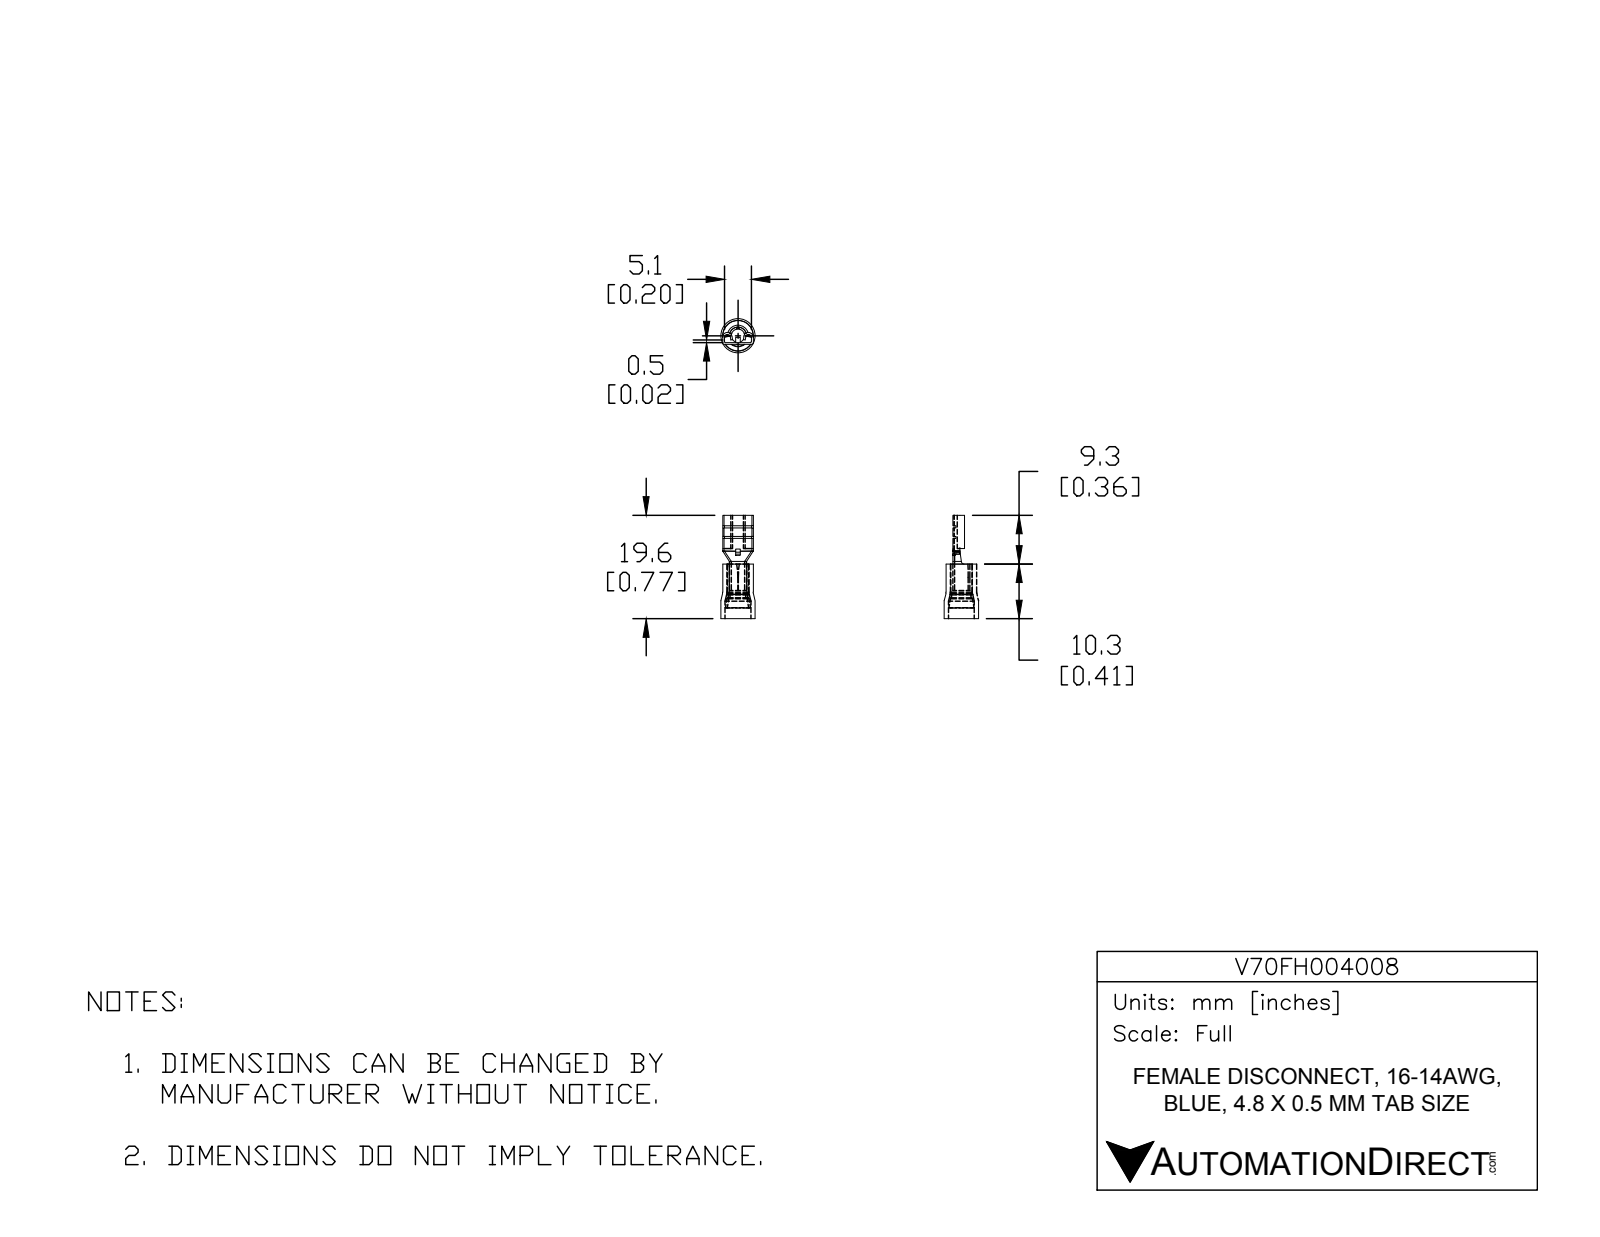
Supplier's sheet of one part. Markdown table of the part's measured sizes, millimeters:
| quantity | value |
| --- | --- |
| part name | V70FH004008 |
| STEP written by | SolidWorks 2017 (AUTOMOTIVE_DESIGN) |
| units | millimeters |
| bodies | 3 solids, 121 faces (49 planar, 38 cylindrical, 34 other) |
| overall size | 19.59 × 6.49 × 6.49 |
| volume | 220 mm³ |
| surface area | 890 mm² |
| round holes (diameter × count) | 2.55 × 1, 3.3 × 1, 4.17 × 1, 4.89 × 1 |
| round bosses / shafts (diameter × count) | 6.49 × 1, 5.77 × 1, 4 × 1, 3.25 × 1 |
| partial cylindrical surfaces (radius × count) | 0.12 × 2, 0.25 × 2, 0.54 × 2, 0.89 × 2, 15.72 × 2, 0.3 × 1, 0.5 × 1, 0.65 × 1 |
| main face-to-face distances | 0.35, 10.34, 5.43, 5.78, 2, 5.08, 2.4, 19.59, 9.25, 0.4 |
